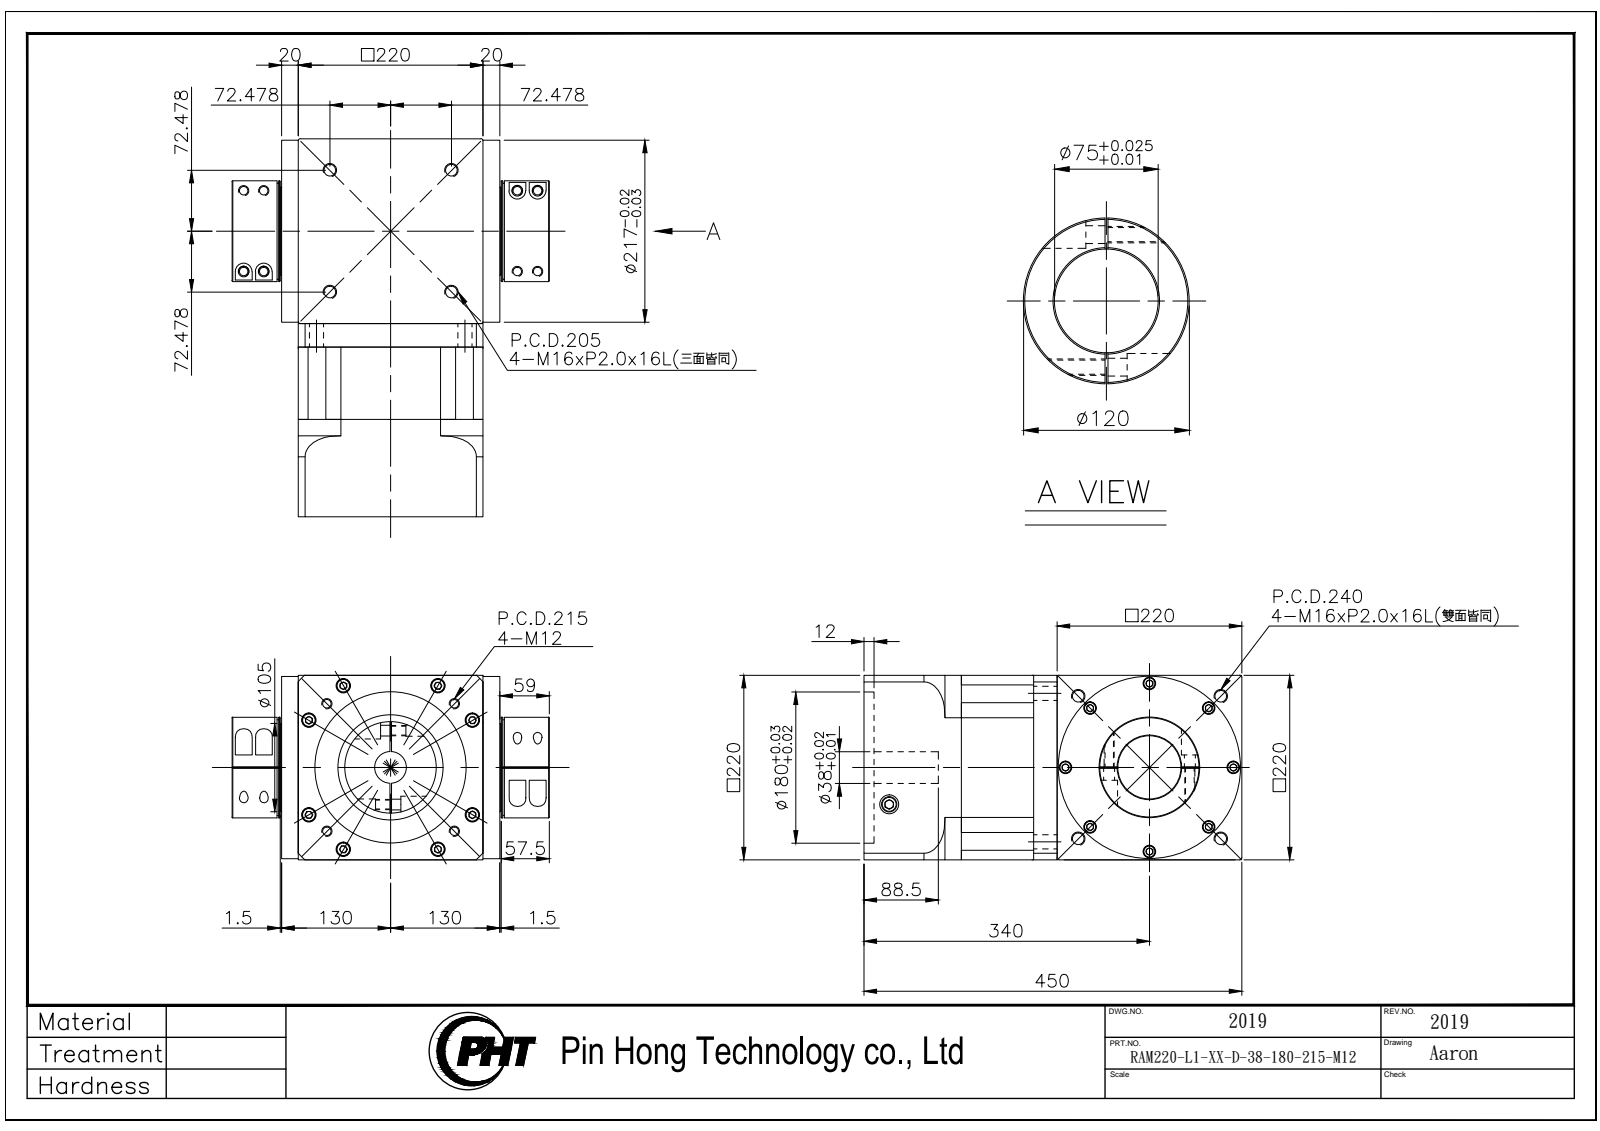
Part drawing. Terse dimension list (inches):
name: RAM220-L1-XX-D-38-180-215-M12_2019
written by: SolidWorks 2016 (AUTOMOTIVE_DESIGN)
unit: in
bodies: 4 solids, 1213 faces (569 planar, 408 cylindrical, 236 other)
size: 17.717 × 14.882 × 8.661
volume: 1 291 in³; area: 1 838 in²
holes: 12× ⌀0.354, 12× ⌀0.551, 12× ⌀0.591, 12× ⌀0.669, 8× ⌀0.433, 8× ⌀0.512, 4× ⌀0.402, 2× ⌀0.886, 1× ⌀1.496, 1× ⌀2.953, 1× ⌀3.567, 1× ⌀3.799
bosses: 12× ⌀0.512, 8× ⌀0.709, 8× ⌀0.63, 8× ⌀0.472, 4× ⌀0.945, 1× ⌀8.543, 1× ⌀4.724, 1× ⌀4.488
rounds: 8× R0.394, 4× R0.591, 1× R4.921, 1× R5.906
face distances: 8.661, 3.386, 1.102, 4.488, 13.15, 9.764, 0.787, 9.449, 5.079, 1.693
hole spacings: 3.937, 2.038, 4.429, 5.568, 6.819, 7.606, 1.147, 1.172
